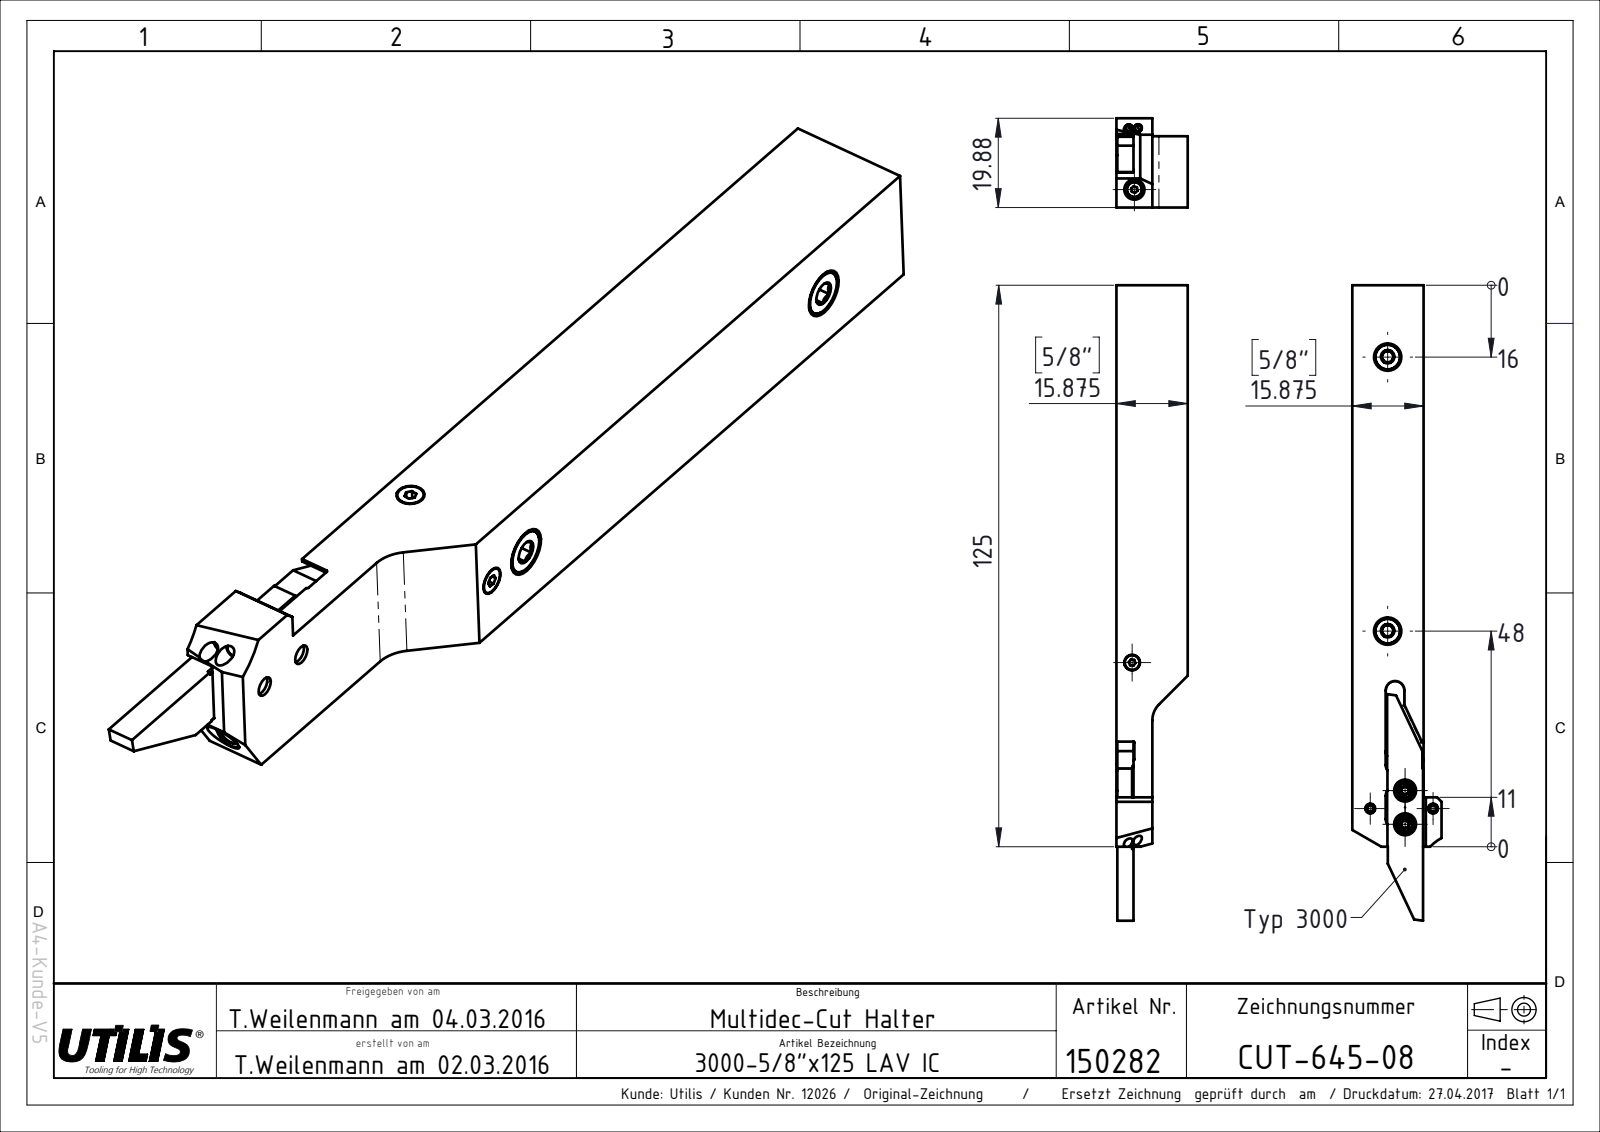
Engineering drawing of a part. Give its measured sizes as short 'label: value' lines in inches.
name: CUT-645-08
written by: SolidWorks 2015 (AUTOMOTIVE_DESIGN)
unit: in
bodies: 1 solid, 226 faces (97 planar, 76 cylindrical, 53 other)
size: 5.704 × 0.783 × 0.625
volume: 1.703 in³; area: 14.61 in²
holes: 2× ⌀0.14, 1× ⌀0.081
bosses: 2× ⌀0.161, 2× ⌀0.118, 1× ⌀0.551
rounds: 19× R0.008, 12× R0.018, 5× R0.083, 4× R0.012, 3× R0.043, 2× R0.006, 2× R0.02, 1× R0.079
face distances: 0.625, 0.315, 0.31, 0.15, 0.307, 0.617, 0.157, 0.165, 0.142, 0.476
hole spacings: 0.295
